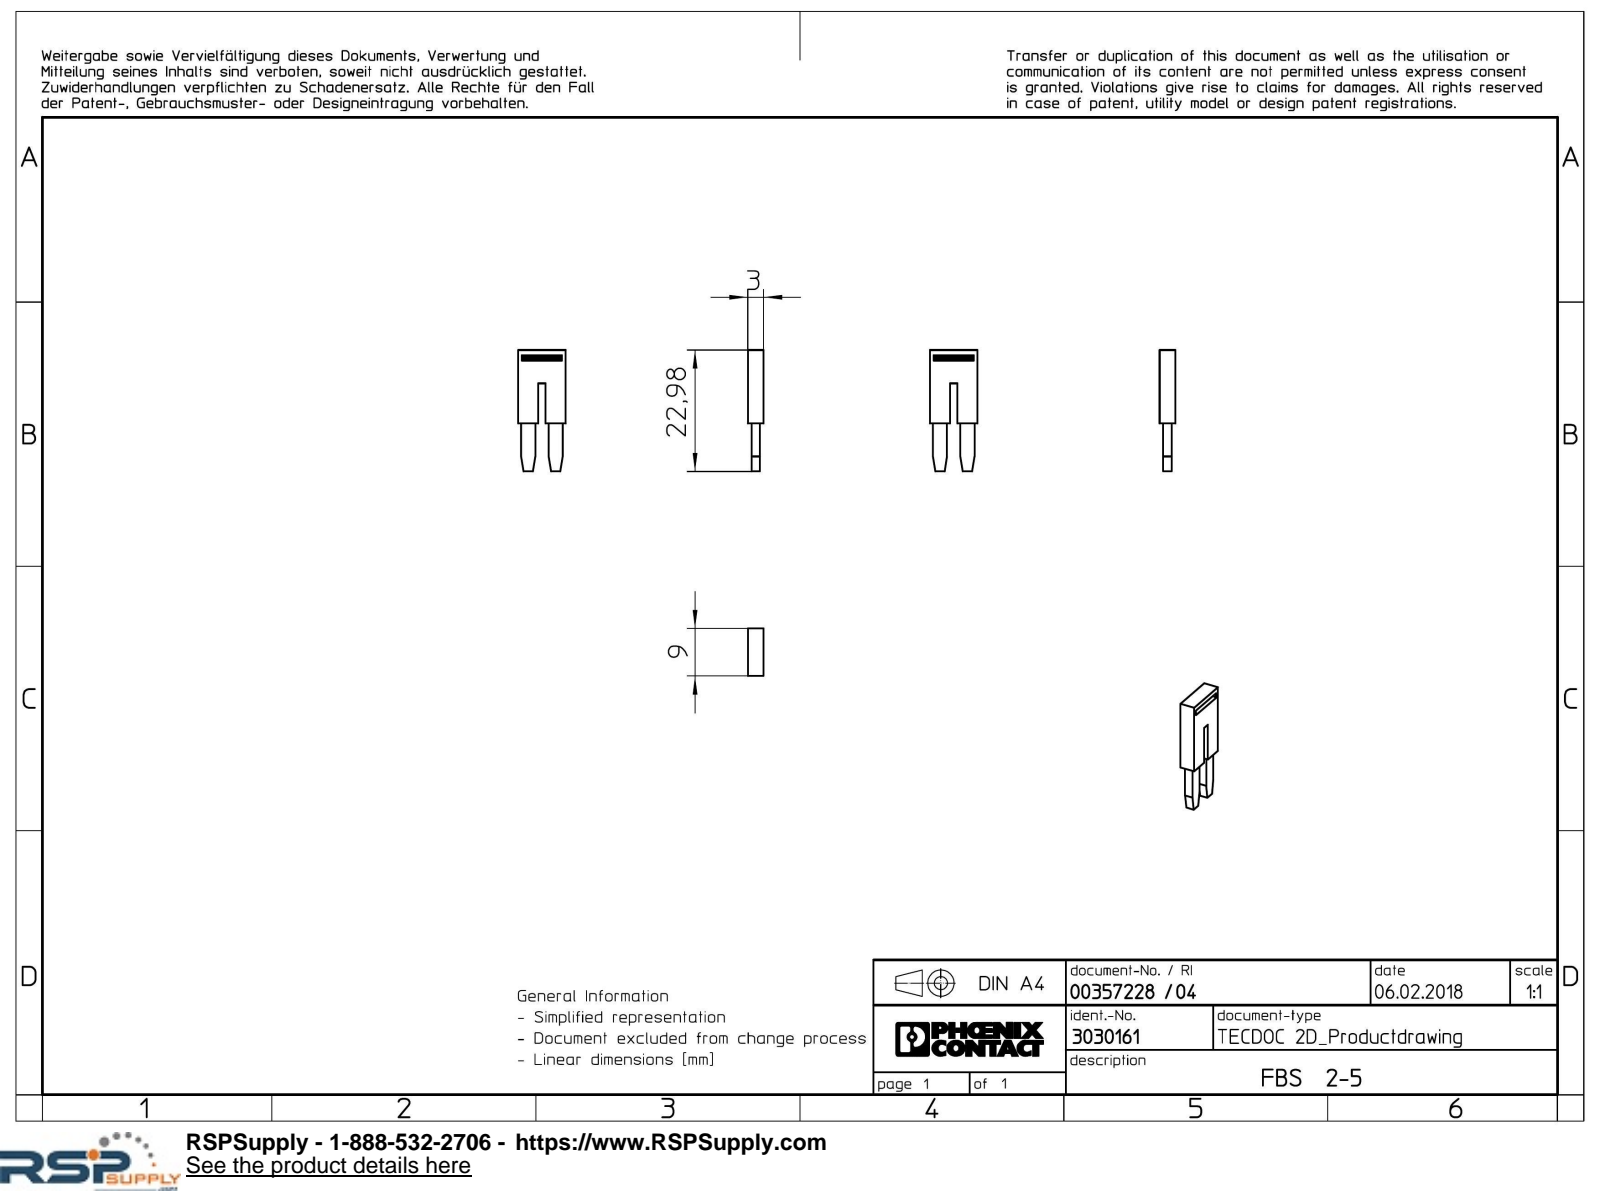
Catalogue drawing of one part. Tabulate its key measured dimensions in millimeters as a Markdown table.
| quantity | value |
| --- | --- |
| part name | FBS_2-5-select |
| STEP written by | Creo Elements/Direct Modeling 20.1A 29-Sep-2018 (C) Parametric Technology GmbH (AUTOMOTIVE_DESIGN) |
| units | millimeters |
| bodies | 1 solid, 34 faces (34 planar, 0 cylindrical, 0 other) |
| overall size | 22.98 × 9 × 3 |
| volume | 407 mm³ |
| surface area | 584 mm² |
| main face-to-face distances | 3, 0.7, 2.3, 5.2, 1.6, 3.8, 9, 0.56, 3.24, 1.4 |
